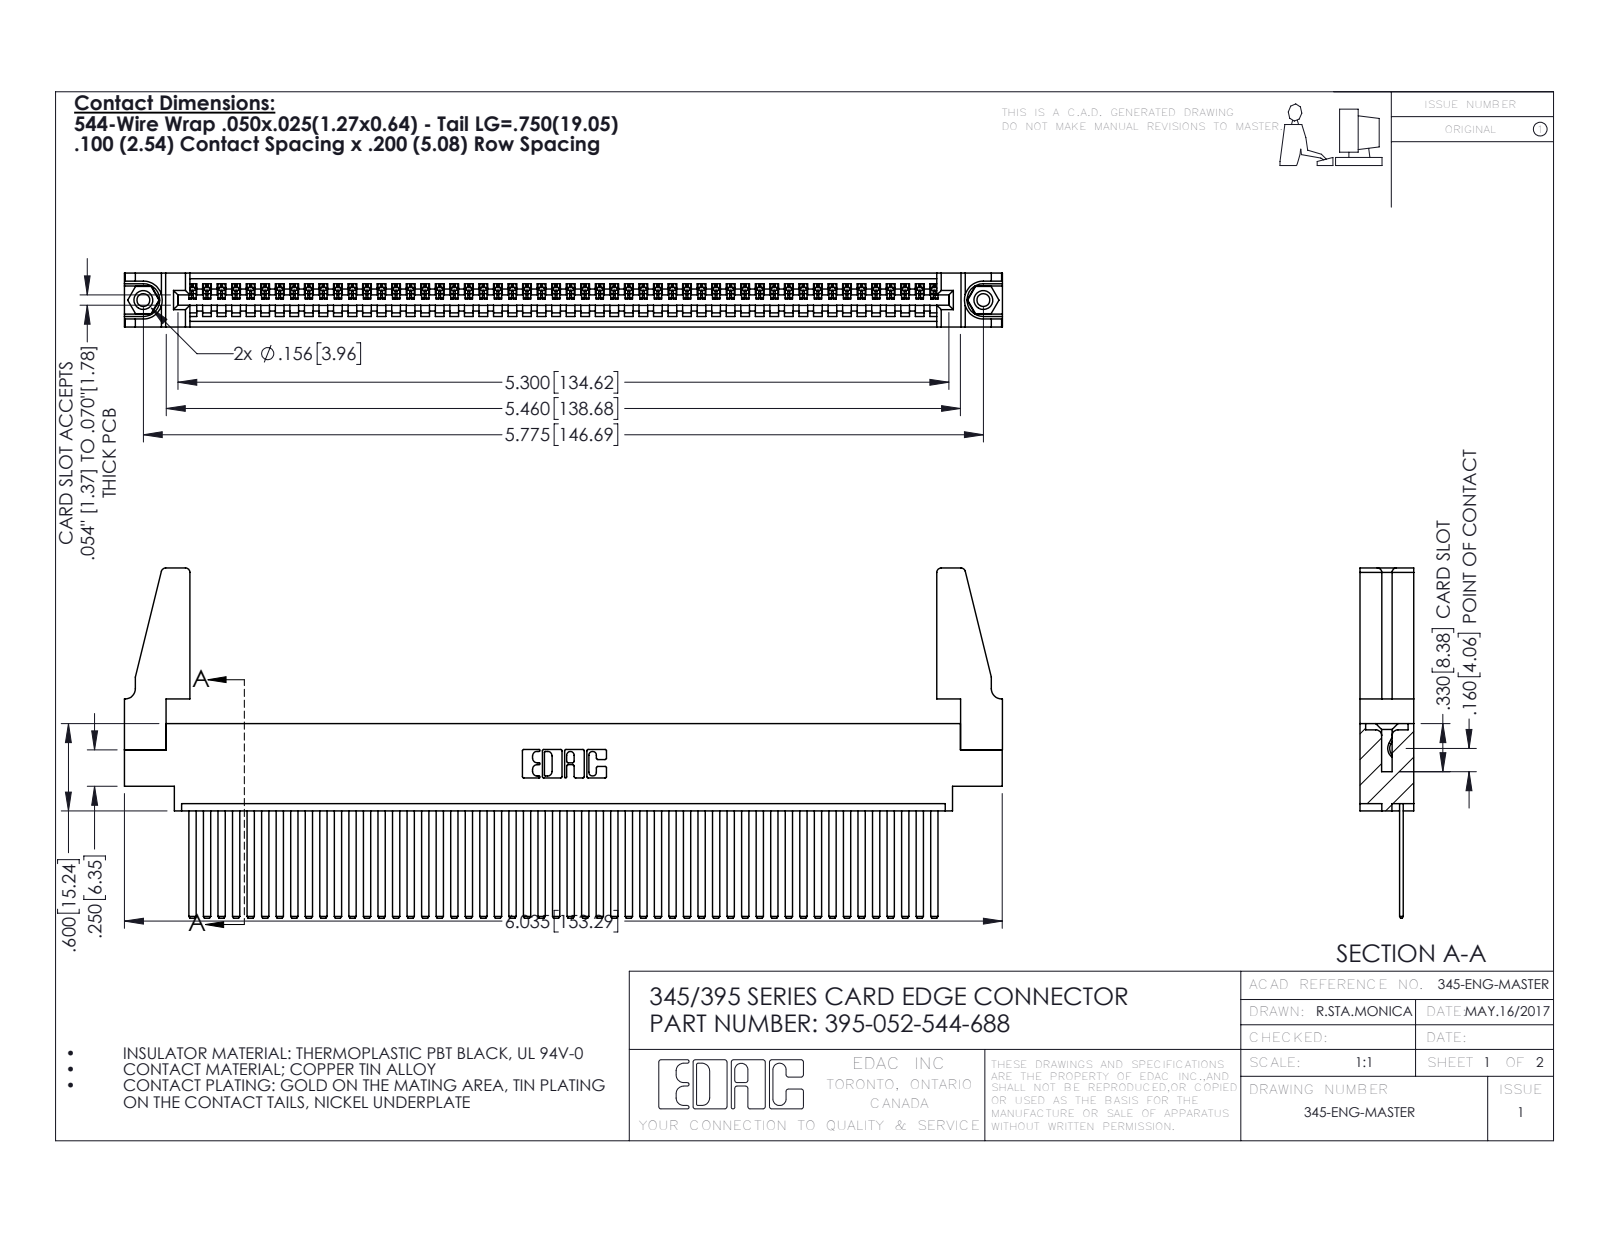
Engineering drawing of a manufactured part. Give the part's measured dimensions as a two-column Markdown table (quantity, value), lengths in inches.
| quantity | value |
| --- | --- |
| part name | 345-250-001_345-250-001-102; 395-052-544-688; 345-220-078_345-220-088; 345-292-001_345-293-144 (+1 more) |
| STEP written by | SolidWorks 2016 (CONFIG_CONTROL_DESIGN) |
| units | inches |
| bodies | 57 solids, 2958 faces (2028 planar, 914 cylindrical, 16 other) |
| overall size | 6.036 × 2.407 × 0.37 |
| volume | 1.122 in³ |
| surface area | 39.23 in² |
| round holes (diameter × count) | 0.089 × 2, 0.125 × 2, 0.156 × 2, 0.064 × 1 |
| round bosses / shafts (diameter × count) | 0.155 × 2 |
| partial cylindrical surfaces (radius × count) | 0.006 × 104, 0.01 × 22, 0.03 × 8, 0.007 × 6, 0.031 × 6, 0.026 × 3, 0.031 × 2, 0.04 × 2 |
| main face-to-face distances | 0.072, 0.298, 0.098, 0.272, 0.025, 0.37, 0.2, 0.225, 0.175, 0.149 |
| hole center spacings | 0.27, 5.539, 5.775 |
